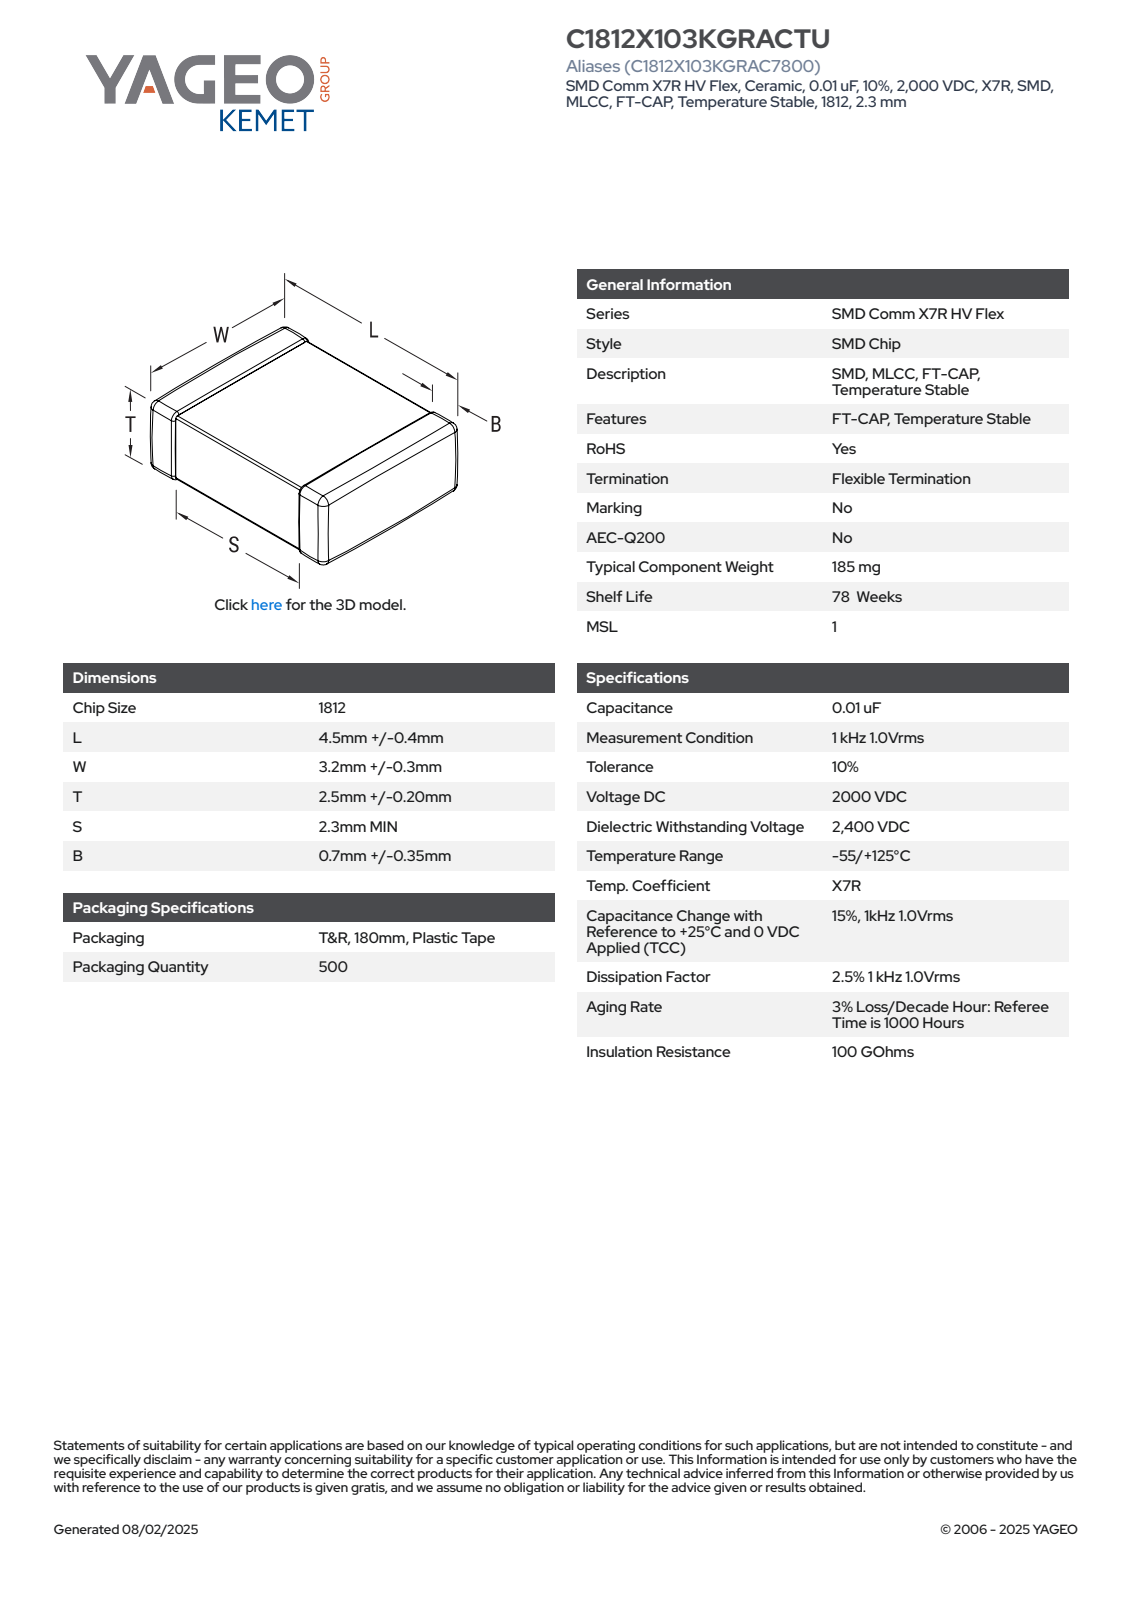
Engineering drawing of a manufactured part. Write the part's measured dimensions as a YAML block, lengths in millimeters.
part_name: "CCS_CCSTDNOS_1812_L4.9W3.5T2.7B1.05"
step_written_by: "SolidWorks 2014 (AUTOMOTIVE_DESIGN)"
units: millimeters
bodies: {solids: 4, faces: 121, planar: 71, cylindrical: 34, other: 16}
overall_size: [4.9, 3.5, 2.7]
volume: 44
surface_area: 78
face_to_face_distances: [2.63, 3.43, 2.56, 4.9, 3.36, 2.7, 3.5, 1.42, 1.94, 1.49]
